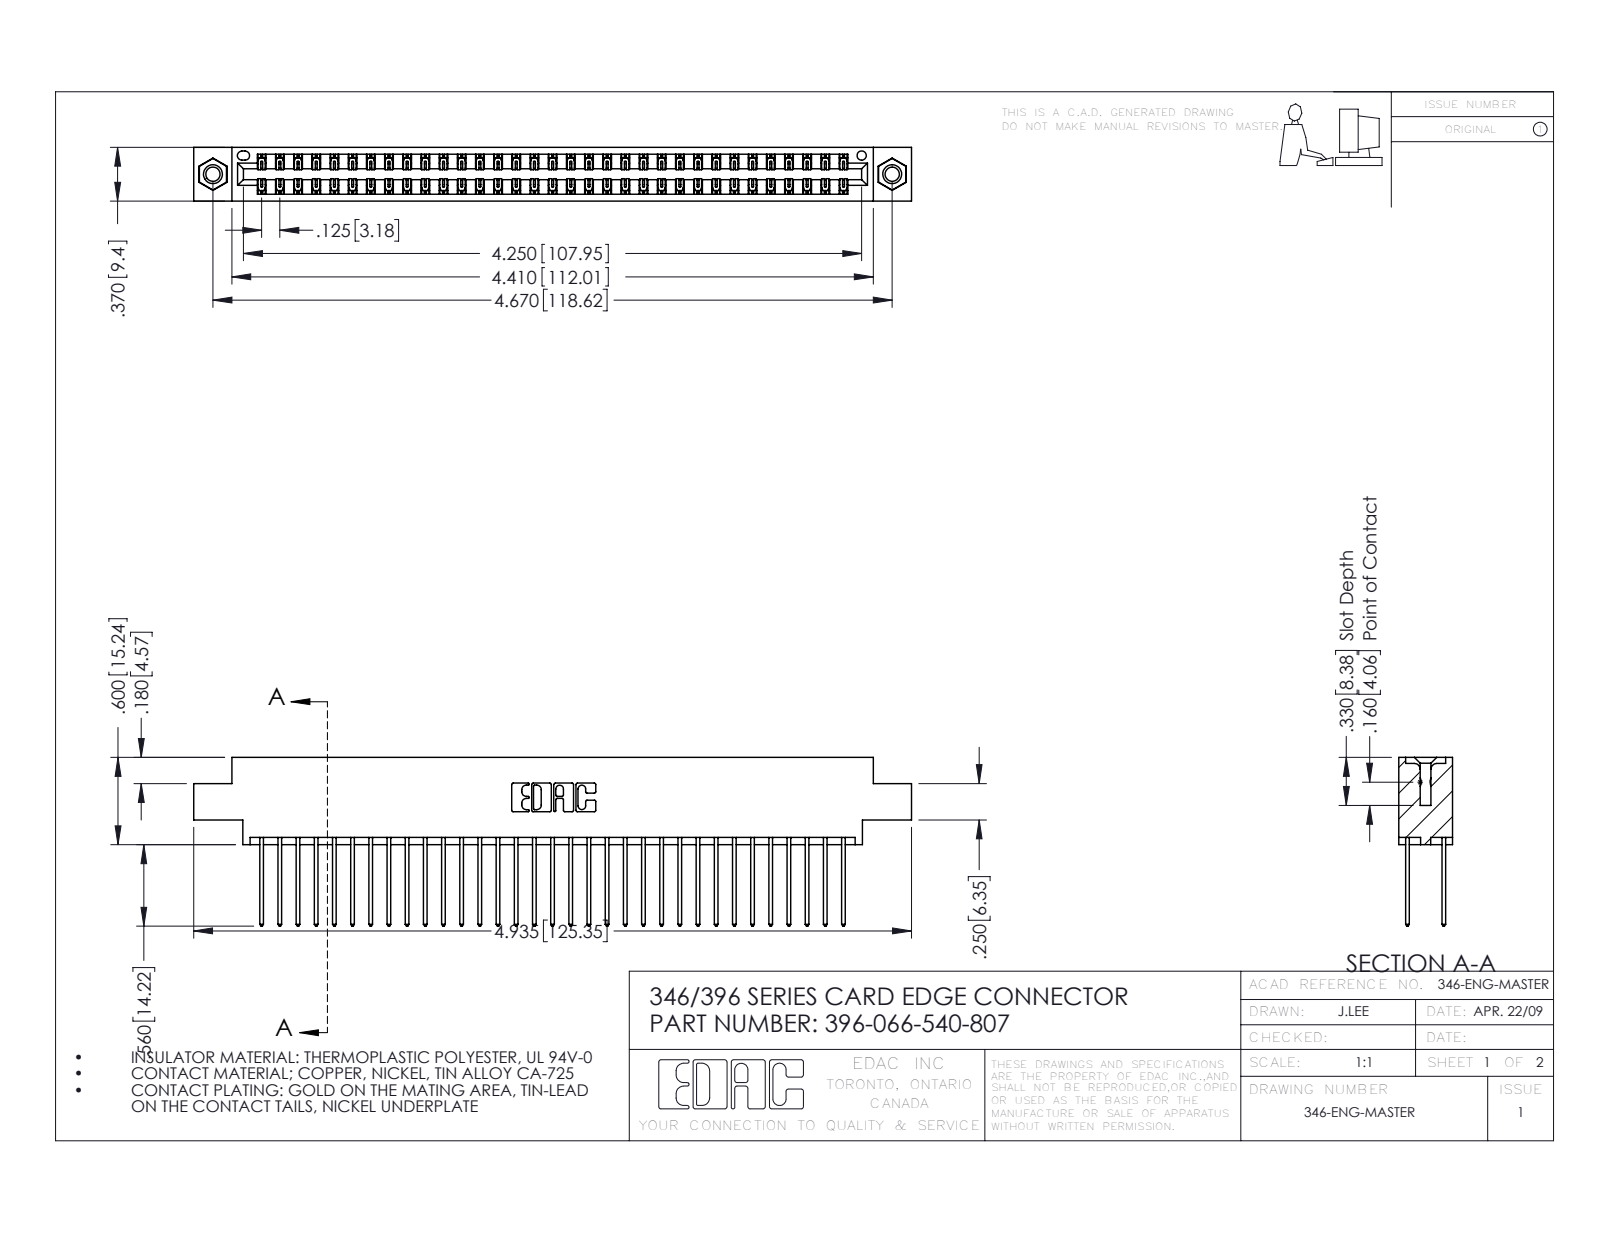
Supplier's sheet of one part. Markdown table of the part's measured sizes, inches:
| quantity | value |
| --- | --- |
| part name | 396-066-540-807; 346 Part_0.170 Offset - 0.156 Dia-TI; 345-250-001_345-250-005-103; 345-292-001_345-293-140 |
| STEP written by | SolidWorks 2016 (CONFIG_CONTROL_DESIGN) |
| units | inches |
| bodies | 69 solids, 3618 faces (2422 planar, 1180 cylindrical, 16 other) |
| overall size | 4.935 × 1.16 × 0.37 |
| volume | 0.747 in³ |
| surface area | 28.01 in² |
| round holes (diameter × count) | 0.098 × 2, 0.125 × 2, 0.156 × 2, 0.064 × 1 |
| round bosses / shafts (diameter × count) | 0.155 × 2 |
| partial cylindrical surfaces (radius × count) | 0.006 × 99, 0.01 × 66, 0.01 × 22, 0.007 × 6, 0.031 × 6, 0.026 × 3, 0.014 × 2, 0.022 × 2 |
| main face-to-face distances | 0.048, 0.322, 0.25, 0.072, 0.298, 0.025, 0.37, 0.275, 0.222, 0.148 |
| hole center spacings | 0.246, 4.462, 4.67 |
